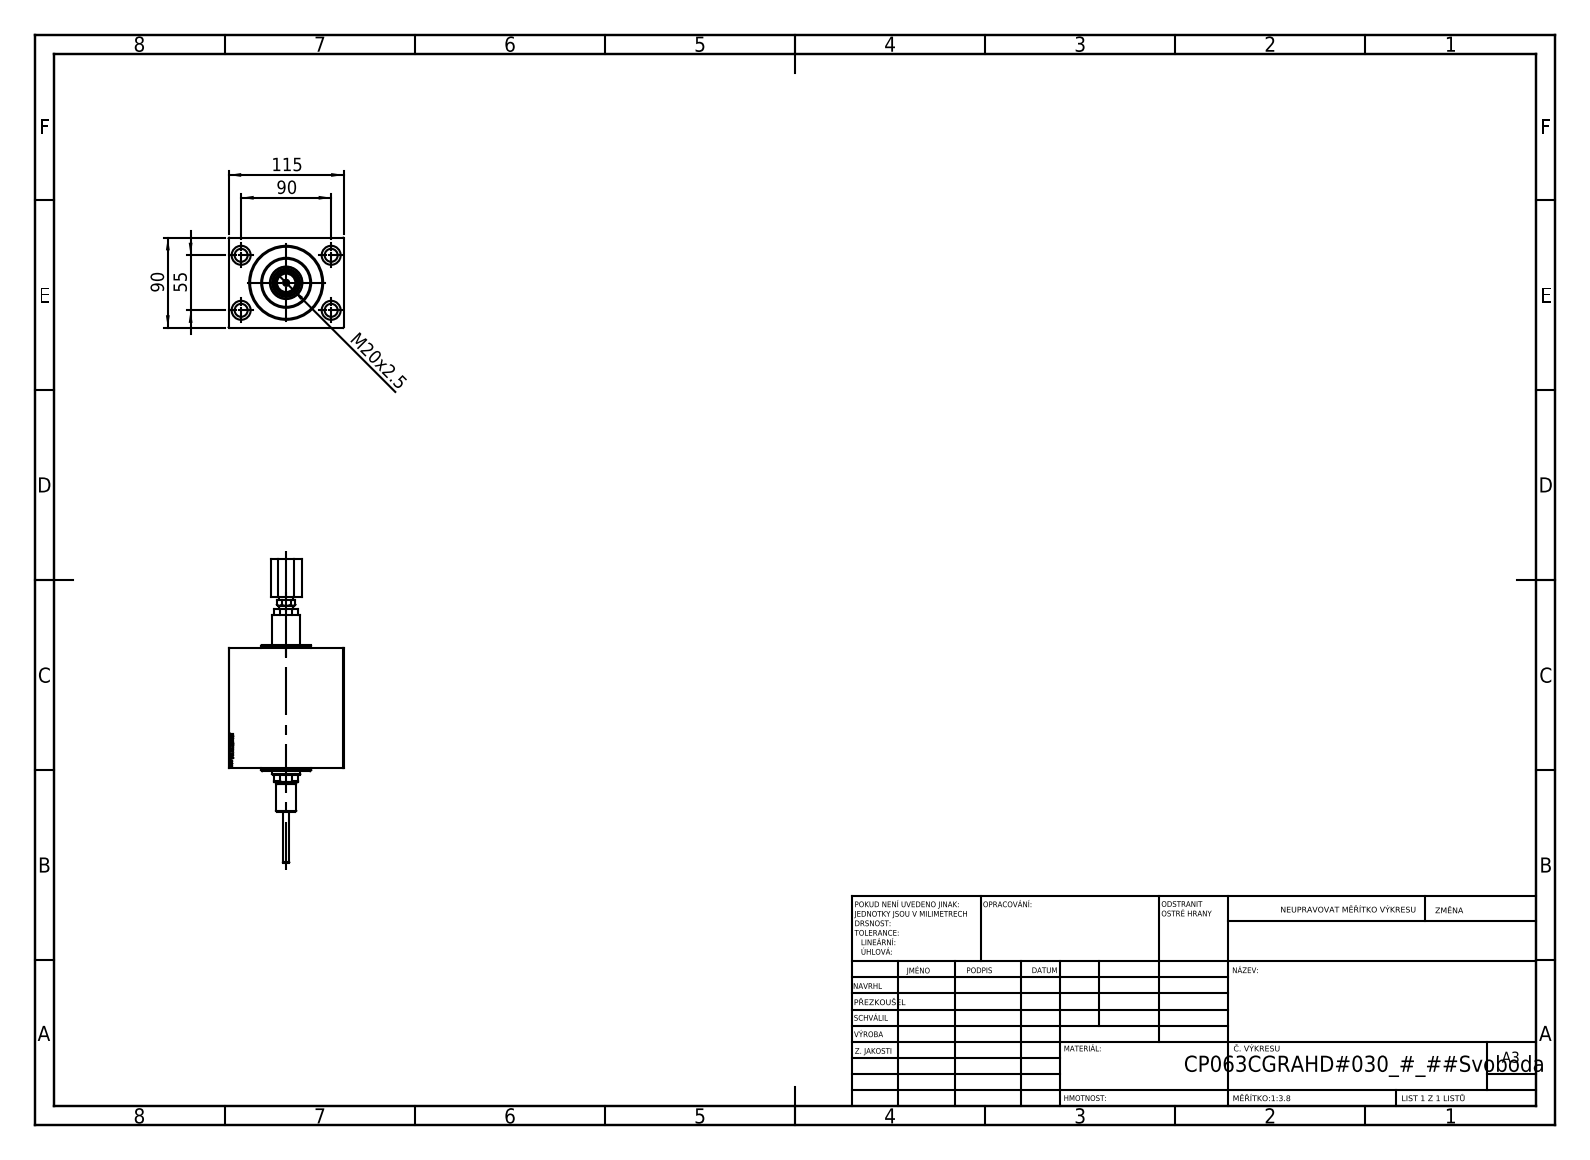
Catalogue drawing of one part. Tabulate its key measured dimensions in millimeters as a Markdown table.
| quantity | value |
| --- | --- |
| part name | V450CP_MALE_METRIC; V450DCP_B_RodCooling_ACCESSORIES; V450DCP_B_VCP; V450DCP_C_Body (+1 more) |
| STEP written by | SolidWorks 2019 (CONFIG_CONTROL_DESIGN) |
| units | millimeters |
| bodies | 5 solids, 966 faces (446 planar, 102 cylindrical, 418 other) |
| overall size | 303.7 × 115 × 90 |
| volume | 1 142 000 mm³ |
| surface area | 176 944 mm² |
| round holes (diameter × count) | 13 × 4, 19 × 4, 6 × 3, 4 × 2, 9.73 × 2, 13.16 × 2, 15 × 2, 3 × 1, 18.5 × 1, 28 × 1, 31.5 × 1, 32.5 × 1 |
| round bosses / shafts (diameter × count) | 50 × 1, 20 × 1, 18 × 1, 13.47 × 1 |
| partial cylindrical surfaces (radius × count) | 13.5 × 1 |
| main face-to-face distances | 90, 115, 102.2, 30, 119.7, 17.5, 1, 118.7, 16.5, 42.2 |
| hole center spacings | 30, 52.74, 82.71, 33, 55, 90, 105.48, 42.22 |
